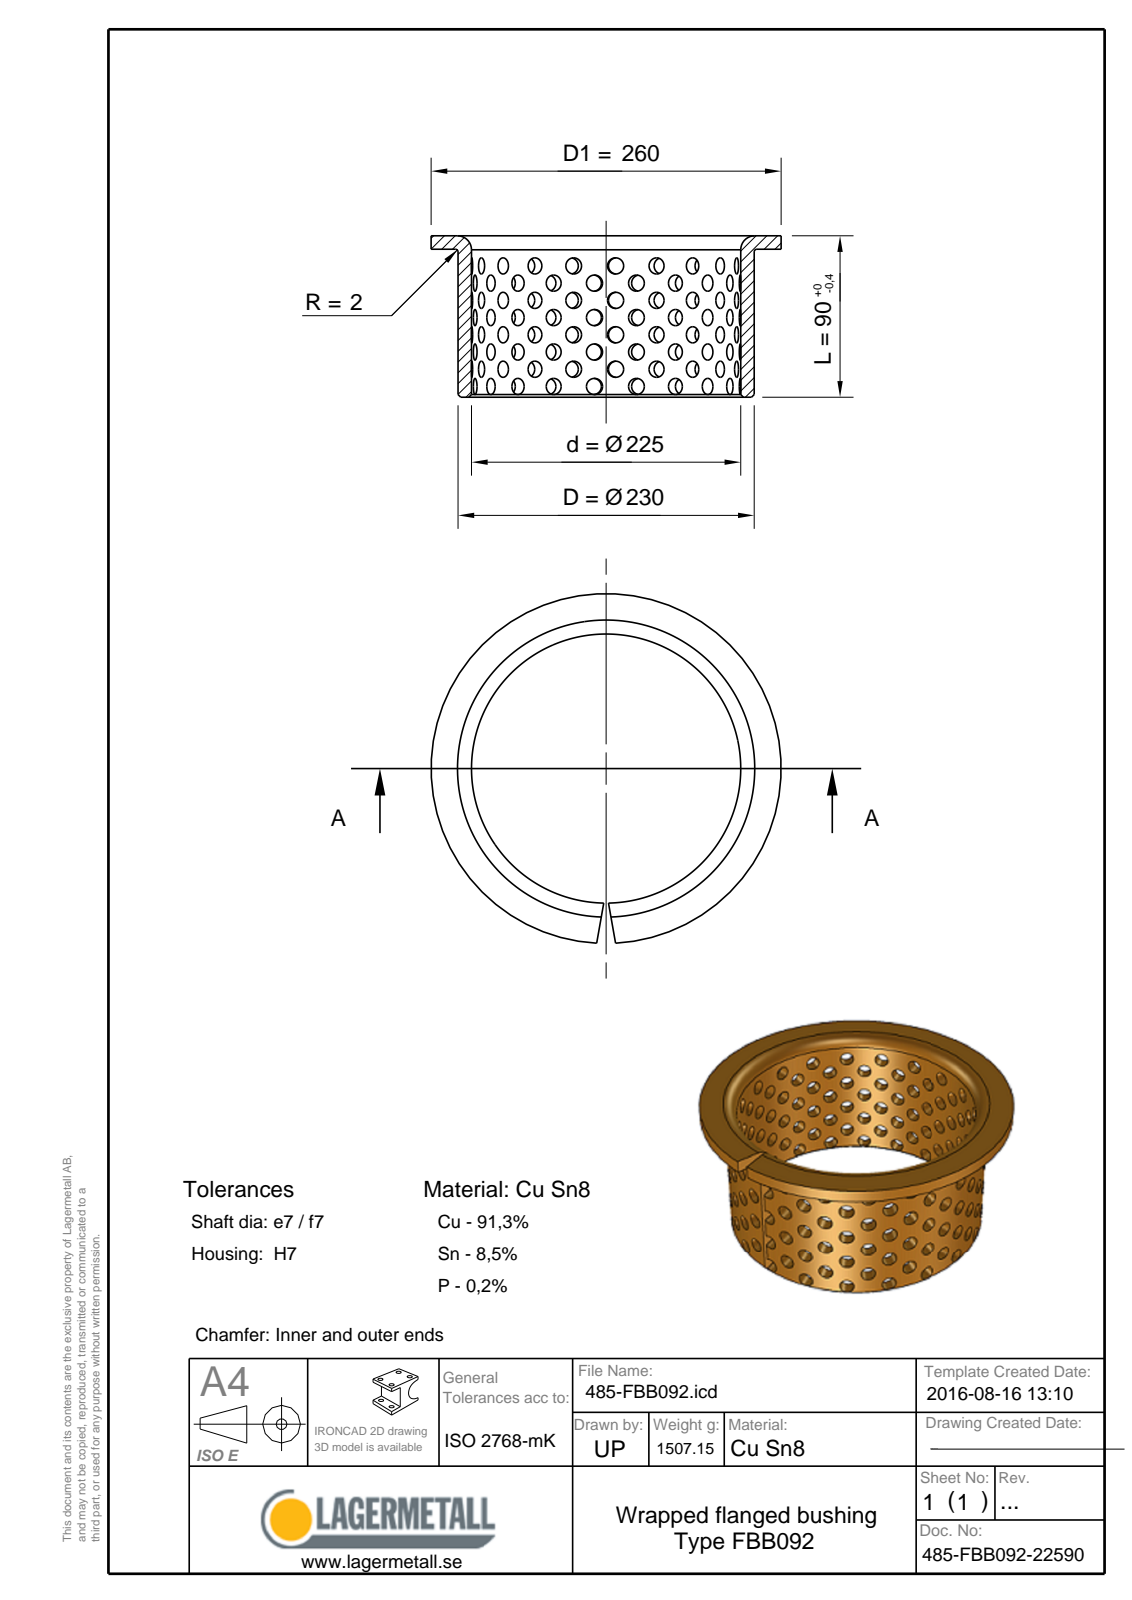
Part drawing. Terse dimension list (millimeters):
name: 485-FBB092-22590
written by: Spatial InterOp 3D (CONFIG_CONTROL_DESIGN)
unit: mm
bodies: 1 solid, 12 faces (5 planar, 3 cylindrical, 4 other)
size: 260 × 259.95 × 90
volume: 186 068 mm³; area: 152 988 mm²
holes: 1× ⌀225
bosses: 1× ⌀260, 1× ⌀230
face distances: 2.5, 87.5, 90
